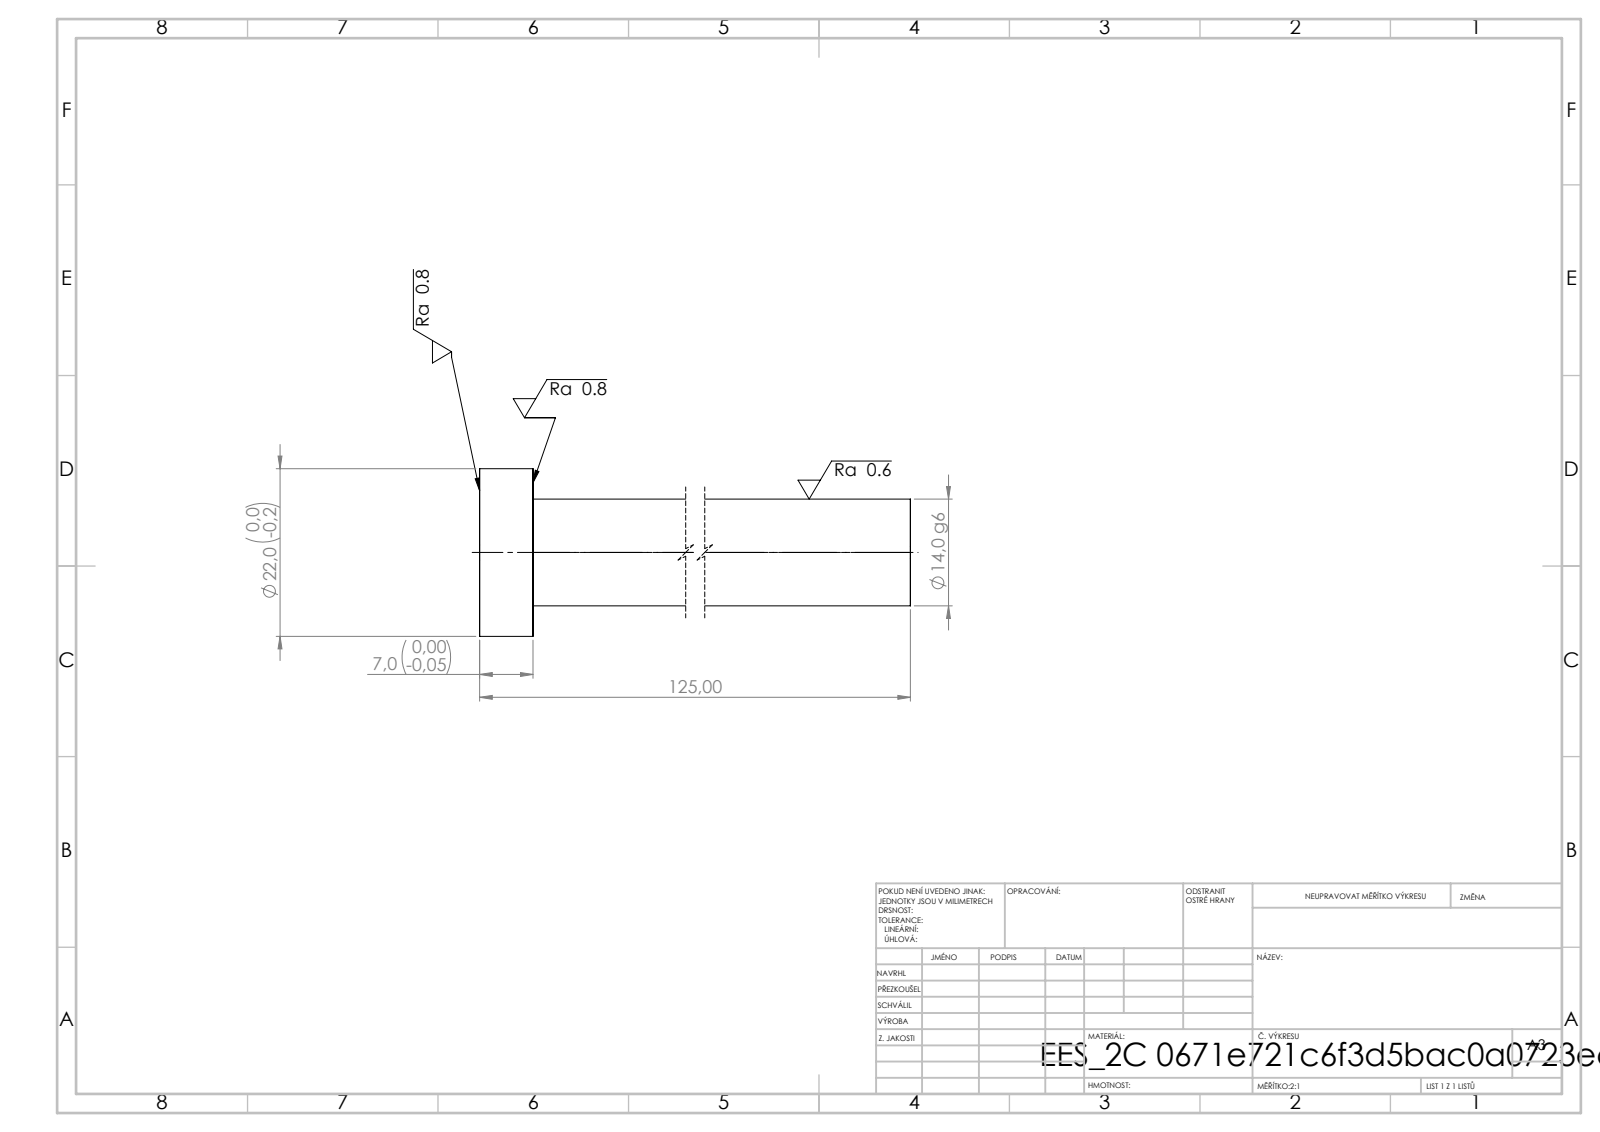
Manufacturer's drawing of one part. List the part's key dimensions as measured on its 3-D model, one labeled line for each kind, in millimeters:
STEP written by: SolidWorks 2019 (CONFIG_CONTROL_DESIGN)
Units: millimetres
Bodies: 1 solid, 7 faces (3 planar, 4 cylindrical, 0 other)
Overall size (bounding box): 125 × 22 × 22
Volume: 20 826 mm³ · Surface area: 6 434 mm²
Round bosses / shafts (diameter × count): ⌀22 ×1, ⌀14 ×1
Main face-to-face distances: 7, 125, 118
